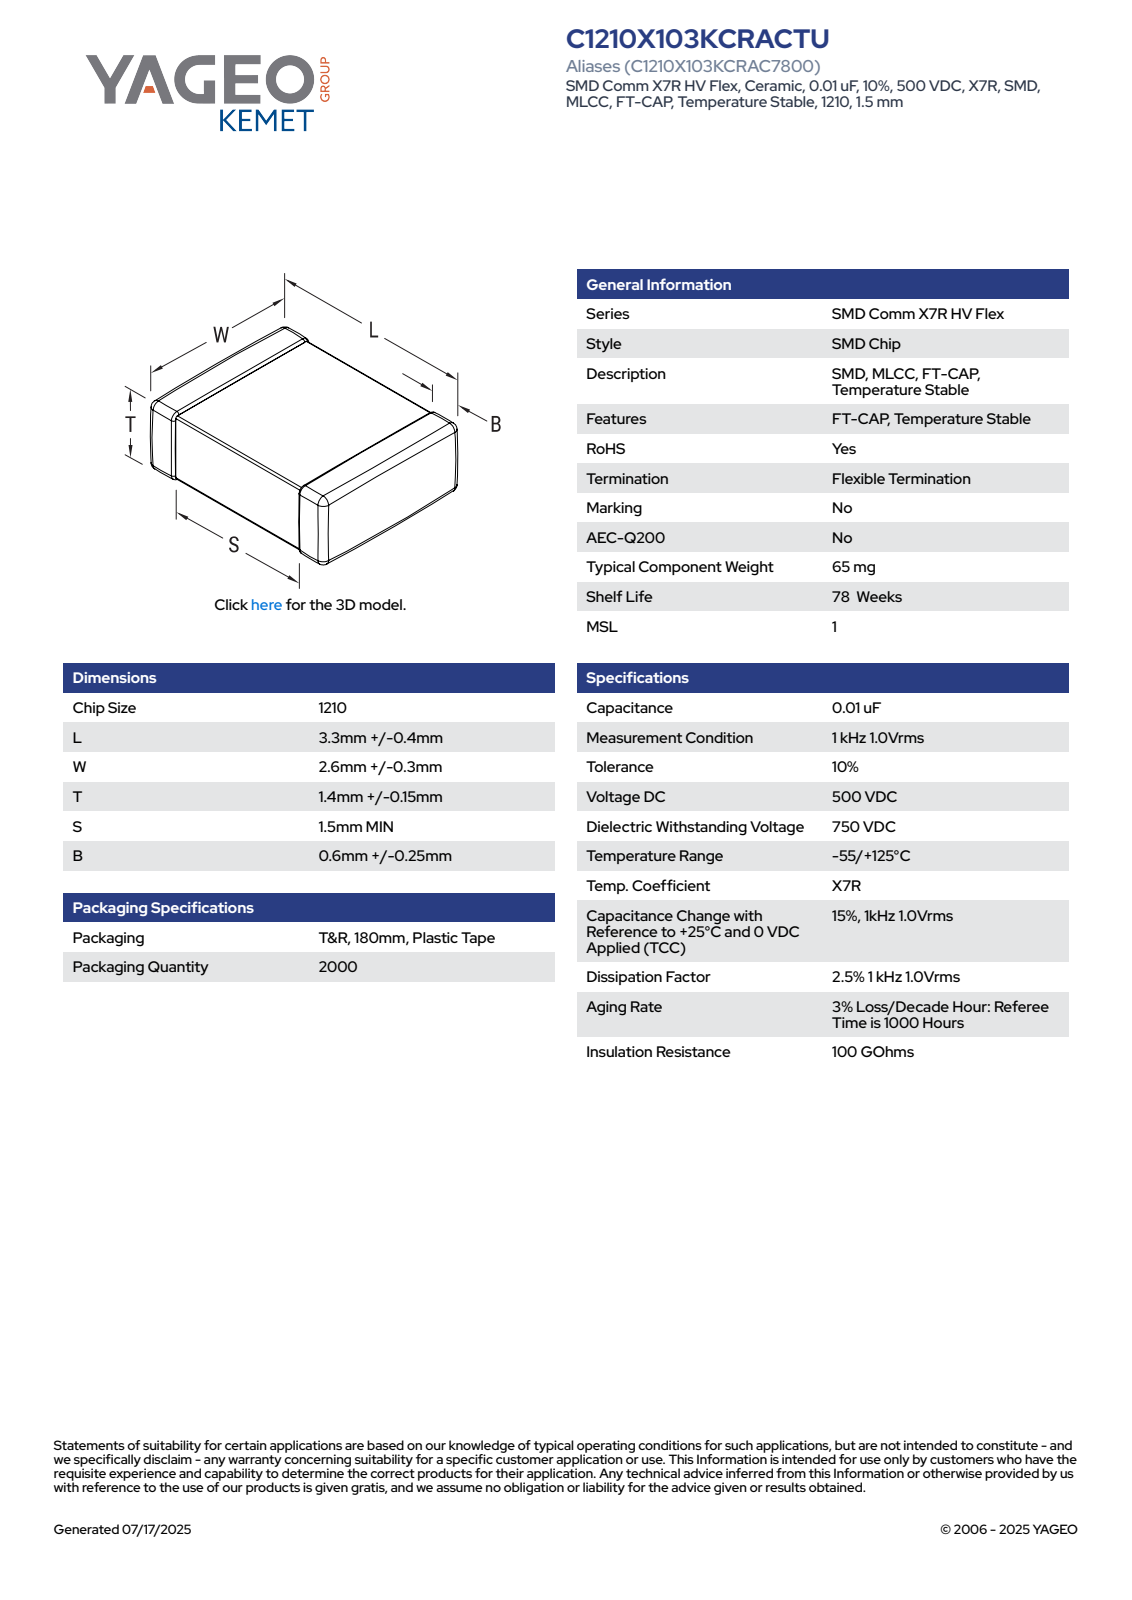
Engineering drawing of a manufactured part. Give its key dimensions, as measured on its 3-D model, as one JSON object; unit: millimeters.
{"part_name": "CCS_CCSTDNOS_1210_L3.7W2.9T1.55B0.85", "step_written_by": "SolidWorks 2014 (AUTOMOTIVE_DESIGN)", "units": "millimeters", "bodies": {"solids": 4, "faces": 125, "planar": 71, "cylindrical": 38, "other": 16}, "overall_size": [3.7, 2.9, 1.55], "volume_mm3": 16, "surface_area_mm2": 41, "face_to_face_distances": [1.49, 1.43, 2.84, 1.55, 3.7, 2.78, 2.9, 1.4, 1.5, 1.34]}
